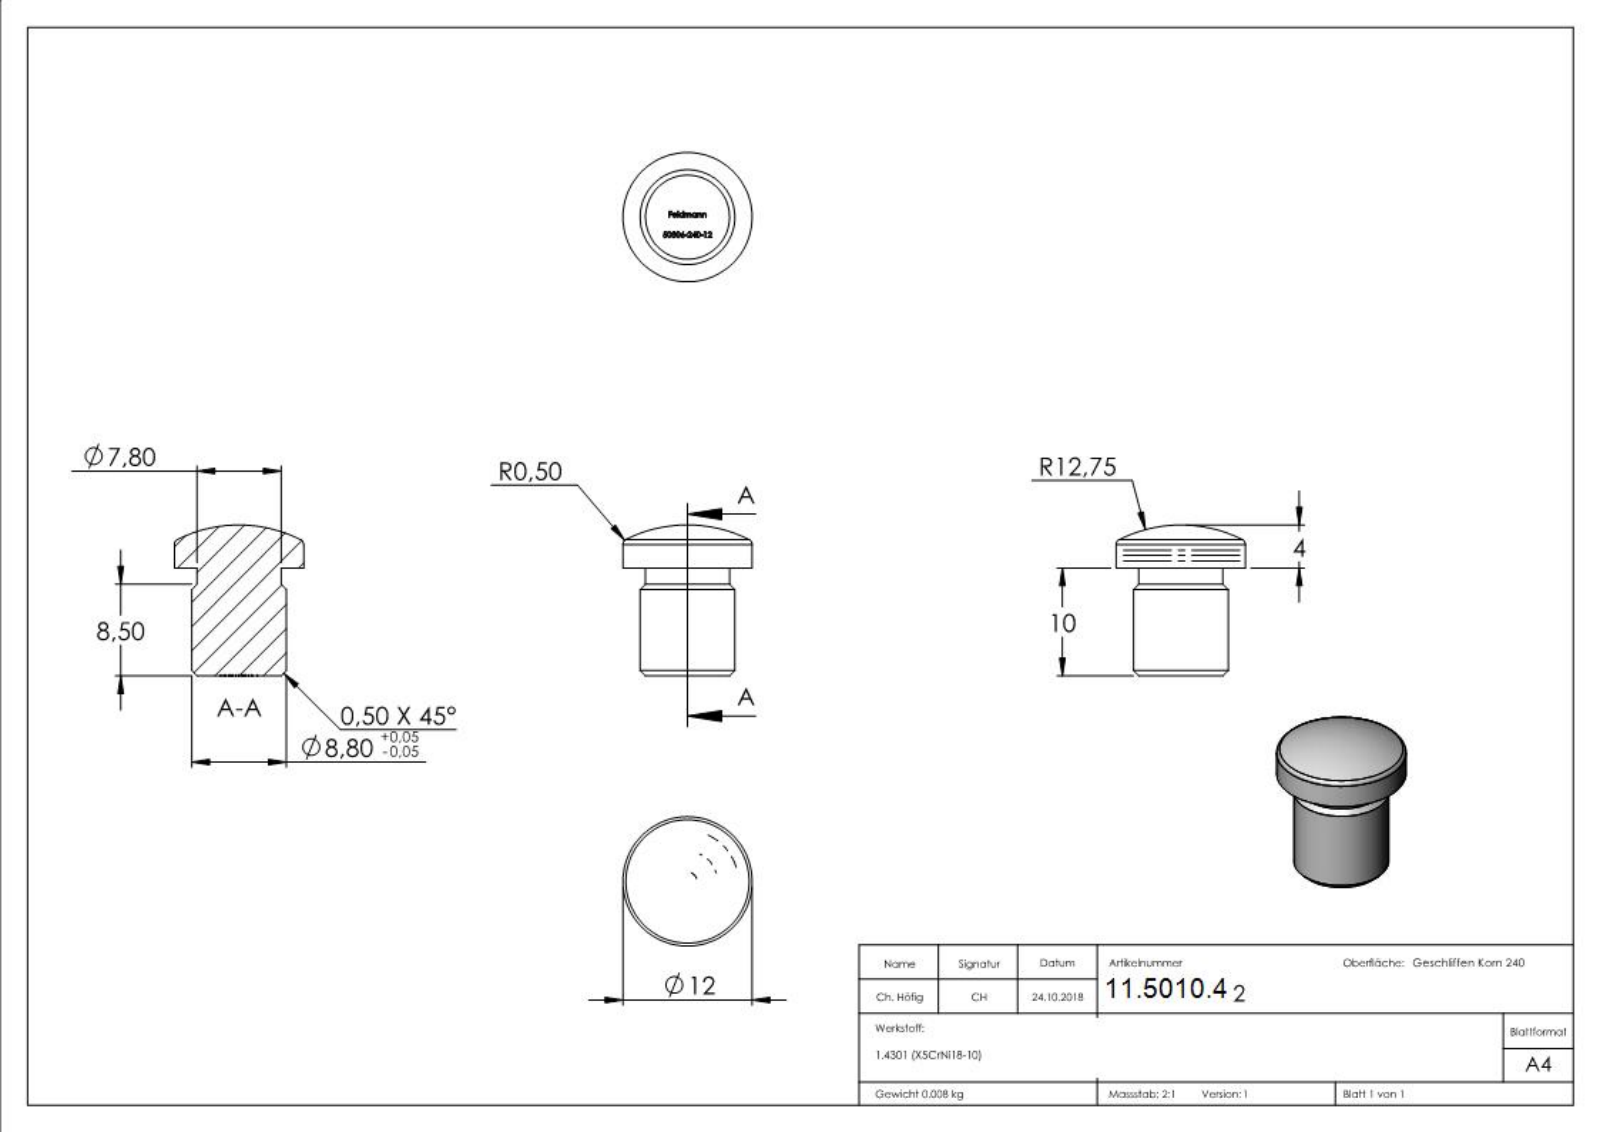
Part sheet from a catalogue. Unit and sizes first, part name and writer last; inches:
Units: inches
Overall size (bounding box): 0.551 × 0.472 × 0.472
Round bosses / shafts (diameter × count): ⌀0.472 ×1, ⌀0.346 ×1, ⌀0.307 ×1
Main face-to-face distances: 0.394, 0.39, 0.028, 0.026, 0.063, 0.074, 0.057, 0.081, 0.047, 0.065
Volume: 0.058 in³ · Surface area: 0.946 in²
Bodies: 1 solid, 269 faces (143 planar, 6 cylindrical, 120 other)
Part name (STEP PRODUCT): 50306-240-12
STEP written by: SolidWorks 2015 (CONFIG_CONTROL_DESIGN)
